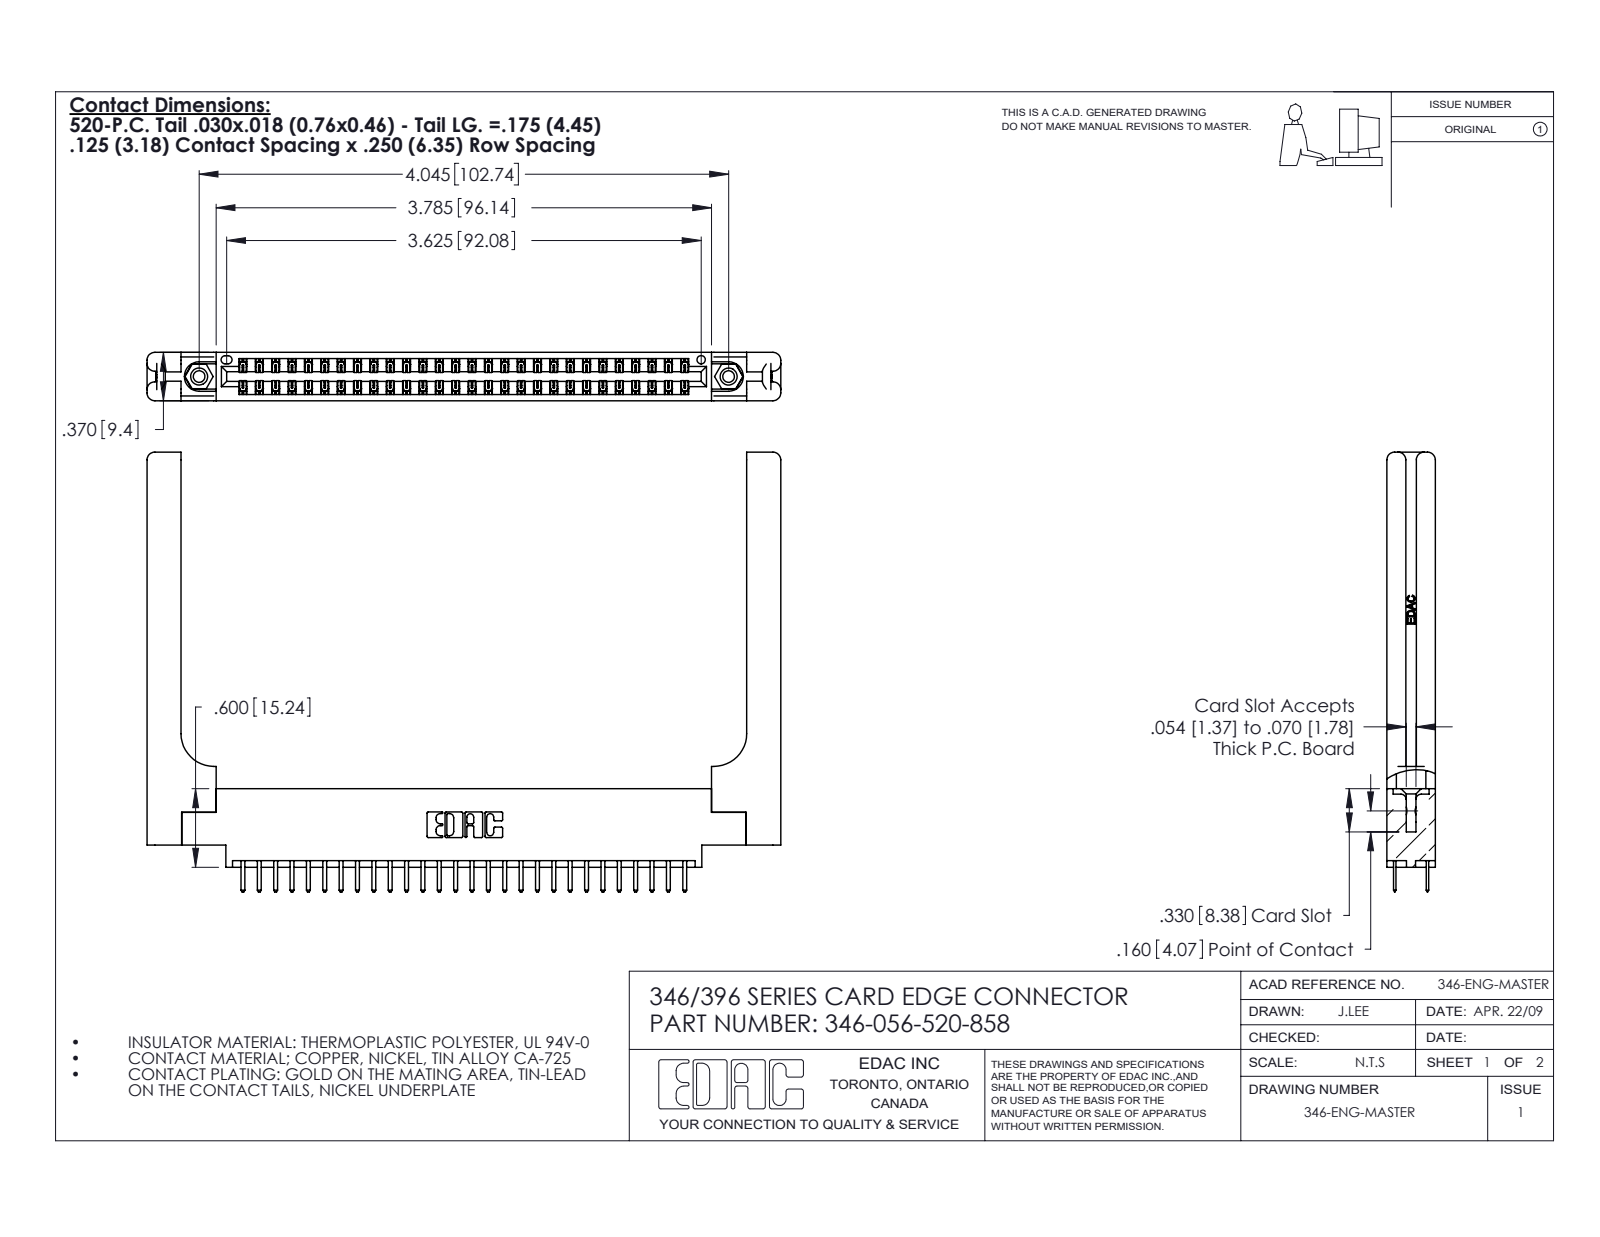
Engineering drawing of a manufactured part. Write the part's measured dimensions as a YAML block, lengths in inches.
part_name: "346-056-520-858; 346 Part_0.170 Offset - 0.156 Dia-TH; 345-292-001_345-293-120; 345-250-001_345-250-001-102 (+1 more)"
step_written_by: "SolidWorks 2020 (CONFIG_CONTROL_DESIGN)"
units: inches
bodies: {solids: 61, faces: 3532, planar: 2314, cylindrical: 1158, other: 60}
overall_size: [4.841, 3.358, 0.37]
volume: 1.17
surface_area: 32.5
round_holes:
  - {diameter: 0.089, count: 2}
  - {diameter: 0.125, count: 2}
  - {diameter: 0.156, count: 2}
  - {diameter: 0.064, count: 1}
round_bosses_or_shafts:
  - {diameter: 0.155, count: 2}
partial_cylinders:
  - {radius: 0.006, count: 84}
  - {radius: 0.01, count: 60}
  - {radius: 0.01, count: 22}
  - {radius: 0.06, count: 16}
  - {radius: 0.007, count: 6}
  - {radius: 0.031, count: 6}
  - {radius: 0.026, count: 3}
  - {radius: 0.014, count: 2}
face_to_face_distances: [0.37, 0.048, 0.322, 0.072, 0.148, 0.15, 0.25, 0.298, 0.025, 0.275]
hole_center_spacings: [0.246, 3.837, 4.045]
